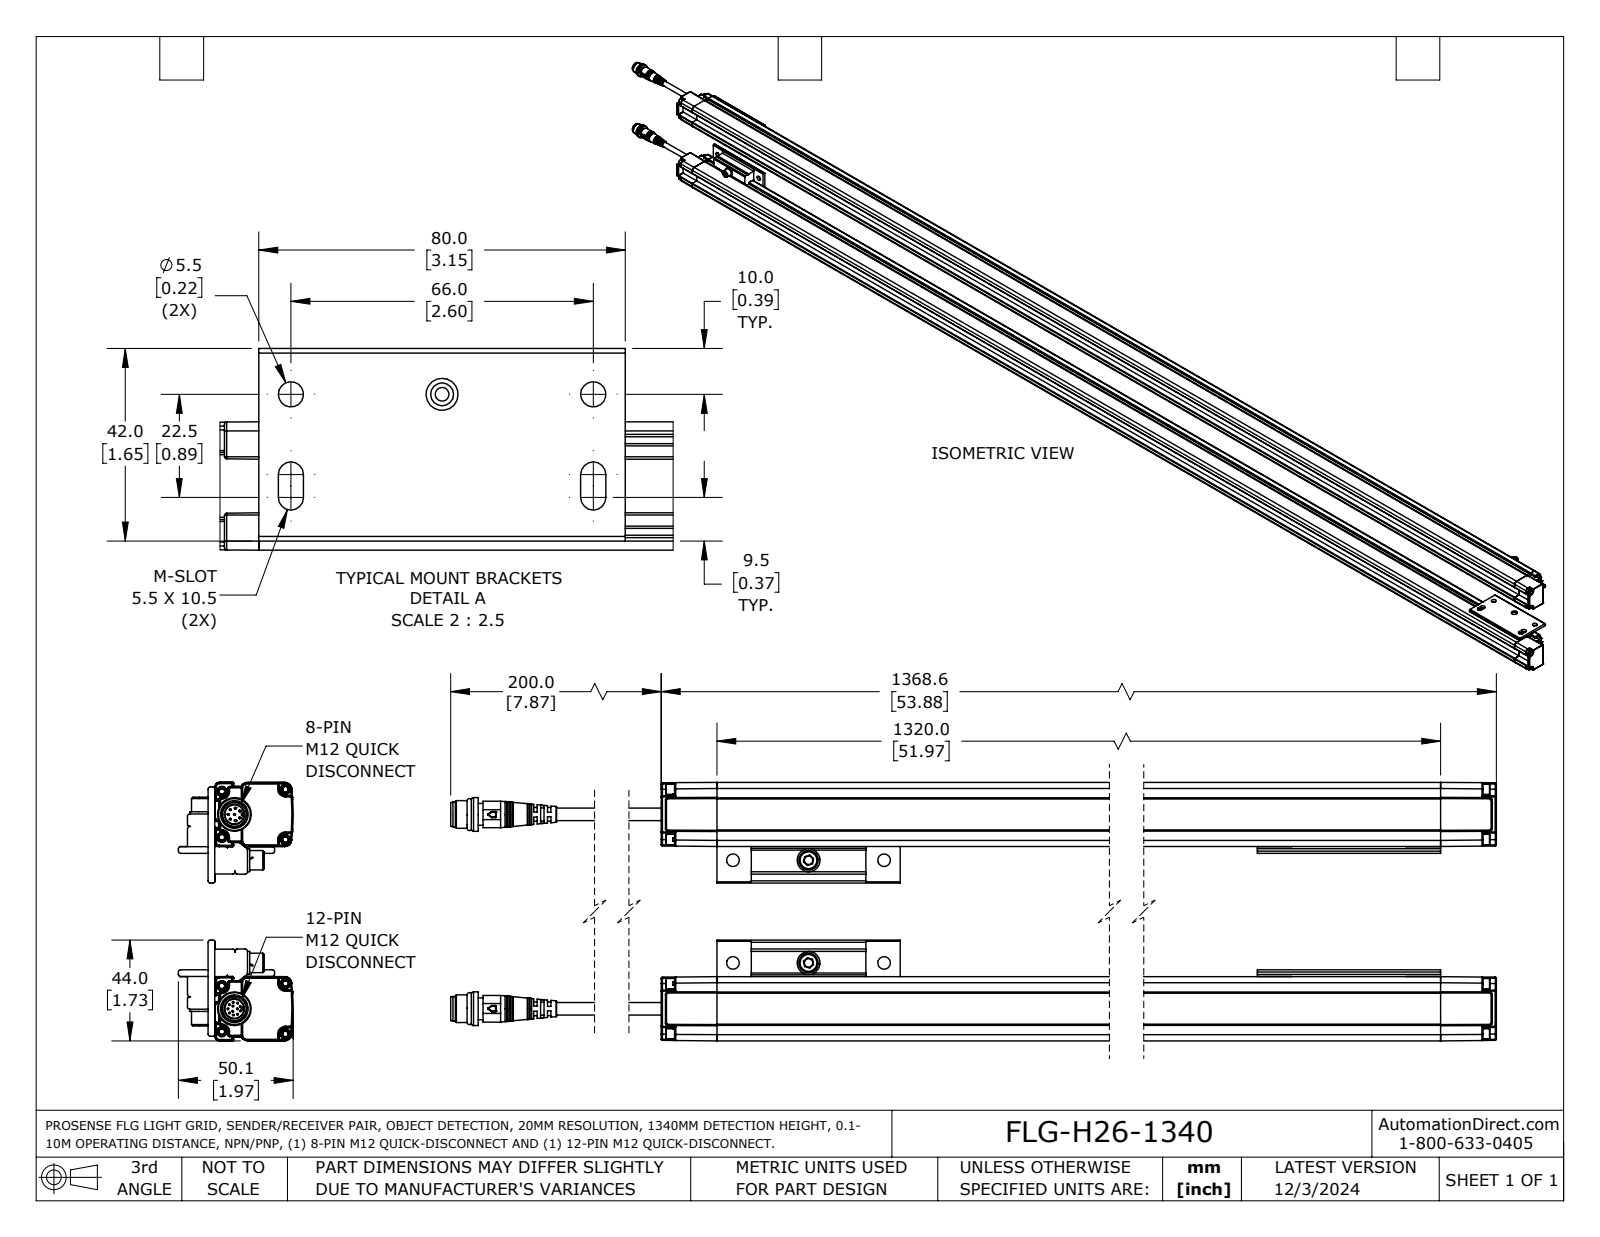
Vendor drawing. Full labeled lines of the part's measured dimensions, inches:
Part name (STEP PRODUCT): FLG-H26-1340
STEP written by: SolidWorks 2023 (CONFIG_CONTROL_DESIGN)
Units: inches
Bodies: 10 solids, 1668 faces (816 planar, 456 cylindrical, 396 other)
Overall size (bounding box): 57.502 × 4.441 × 1.972
Volume: 133.9 in³ · Surface area: 831.7 in²
Round holes (diameter × count): ⌀0.016 ×16, ⌀0.217 ×6, ⌀0.098 ×4, ⌀0.197 ×3, ⌀0.327 ×2
Round bosses / shafts (diameter × count): ⌀0.031 ×20, ⌀0.177 ×8, ⌀0.118 ×8, ⌀0.217 ×4, ⌀0.059 ×4, ⌀0.394 ×3, ⌀0.335 ×3, ⌀0.146 ×3
Partial cylindrical surfaces — rounded edges, fillets, slot ends (radius × count): R0.02 ×142, R0.039 ×40, R0.01 ×20, R0.008 ×12, R0.012 ×12, R0.108 ×12, R0.1 ×6, R0.049 ×4
Main face-to-face distances: 3.339, 1.102, 0.071, 0.285, 0.817, 0.97, 2.236, 4.441, 1.041, 0.215
Hole centre spacings: 0.108, 1.299, 0.163, 0.979, 2.191, 0.215, 1.764, 2.598
